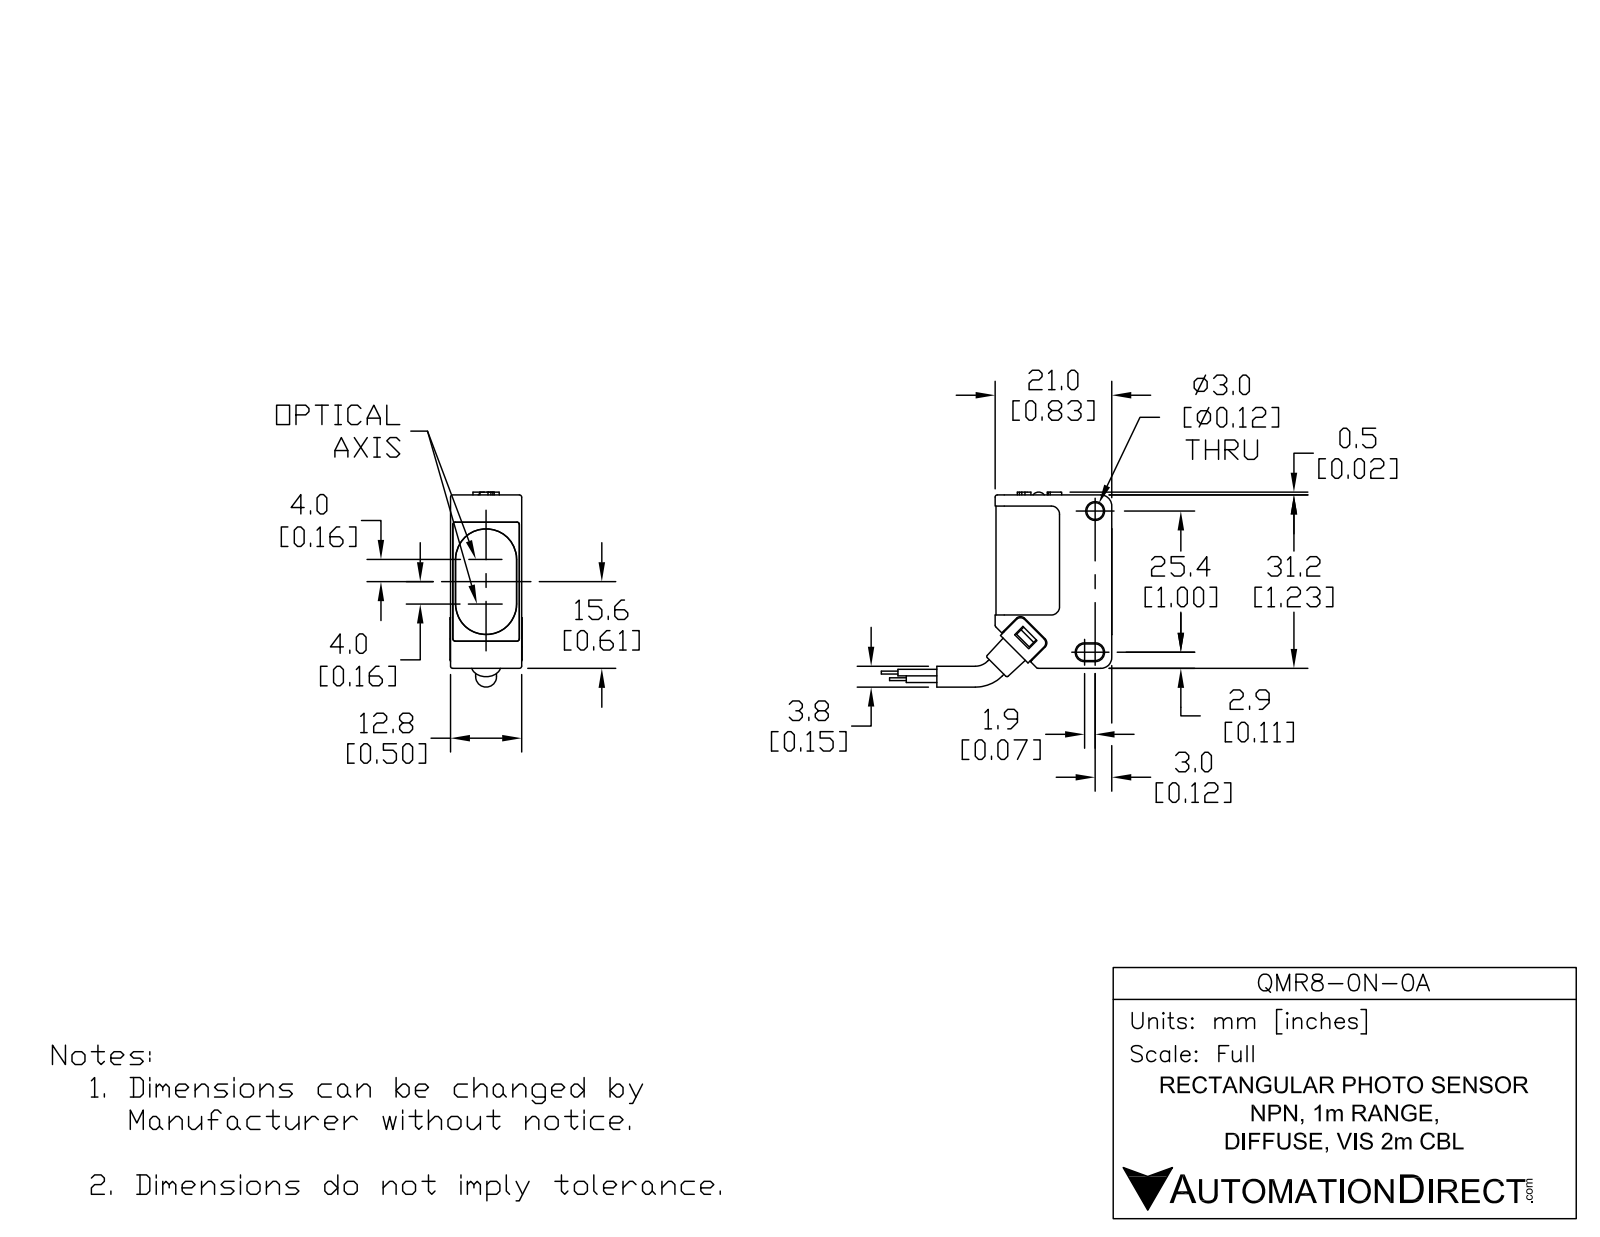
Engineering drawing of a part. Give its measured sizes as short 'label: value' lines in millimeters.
name: QMR8-0N-0A
written by: SolidWorks 2017 (AUTOMOTIVE_DESIGN)
unit: mm
bodies: 9 solids, 258 faces (134 planar, 100 cylindrical, 24 other)
size: 81.1 × 26.2 × 13
volume: 7 700 mm³; area: 5 403 mm²
holes: 3× ⌀3, 1× ⌀3.8, 1× ⌀5.7, 1× ⌀7.2
bosses: 2× ⌀3.5
rounds: 13× R0.4, 10× R0.5, 8× R1, 6× R1.5, 4× R0.6, 2× R0.2, 2× R0.9, 2× R1.1
face distances: 0.5, 12.6, 1.5, 0.4, 12.8, 3.5, 12.4, 2, 12.2, 12.5
hole spacings: 5.2
